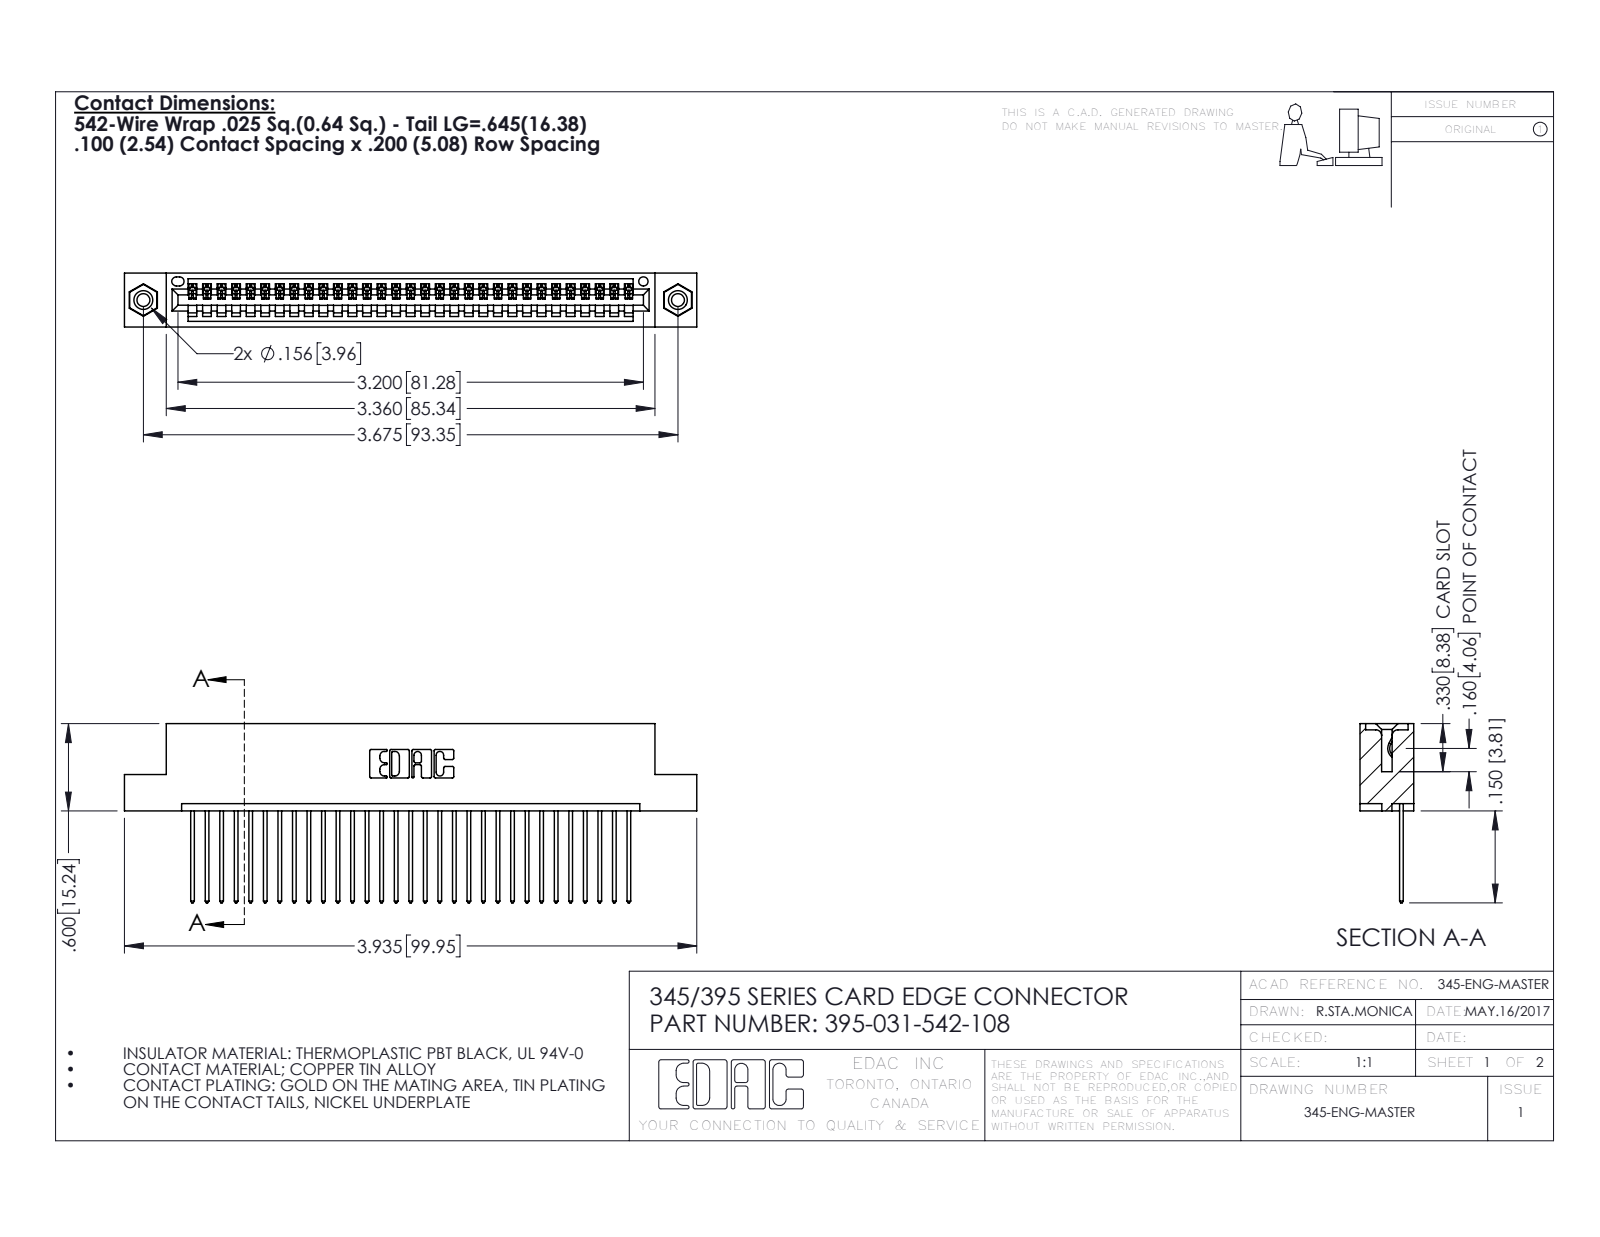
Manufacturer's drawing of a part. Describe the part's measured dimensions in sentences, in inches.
The part is named "395-031-542-108; 345-292-001_345-293-142; 345-250-001_345-250-003-102; 345 Part_Flush Mounting Lugs - 0.156 Dia-TI". Its 3-D file was written by "SolidWorks 2016 (CONFIG_CONTROL_DESIGN)". It is 34 solids with 1984 faces: 1352 planar, 616 cylindrical and 16 other. Overall it measures 3.935 by 1.232 by 0.37 inches. Its volume is 0.578 cubic inches and its surface area 19.97 square inches. Round holes: 2 of diameter 0.089, 2 of diameter 0.125, 2 of diameter 0.156, 1 of diameter 0.064. Round bosses or shafts: 2 of diameter 0.155. Partial cylindrical surfaces (rounded edges, fillets, slot ends): 62 of radius 0.006, 62 of radius 0.01, 22 of radius 0.01, 6 of radius 0.007, 6 of radius 0.031, 3 of radius 0.026, 2 of radius 0.031, 2 of radius 0.04. The main face-to-face distances are 0.072, 0.298, 0.2, 0.37, 0.098, 0.272, 0.025, 0.225, 0.149, 0.072. The hole center spacings are 0.27, 3.44, 3.675.
